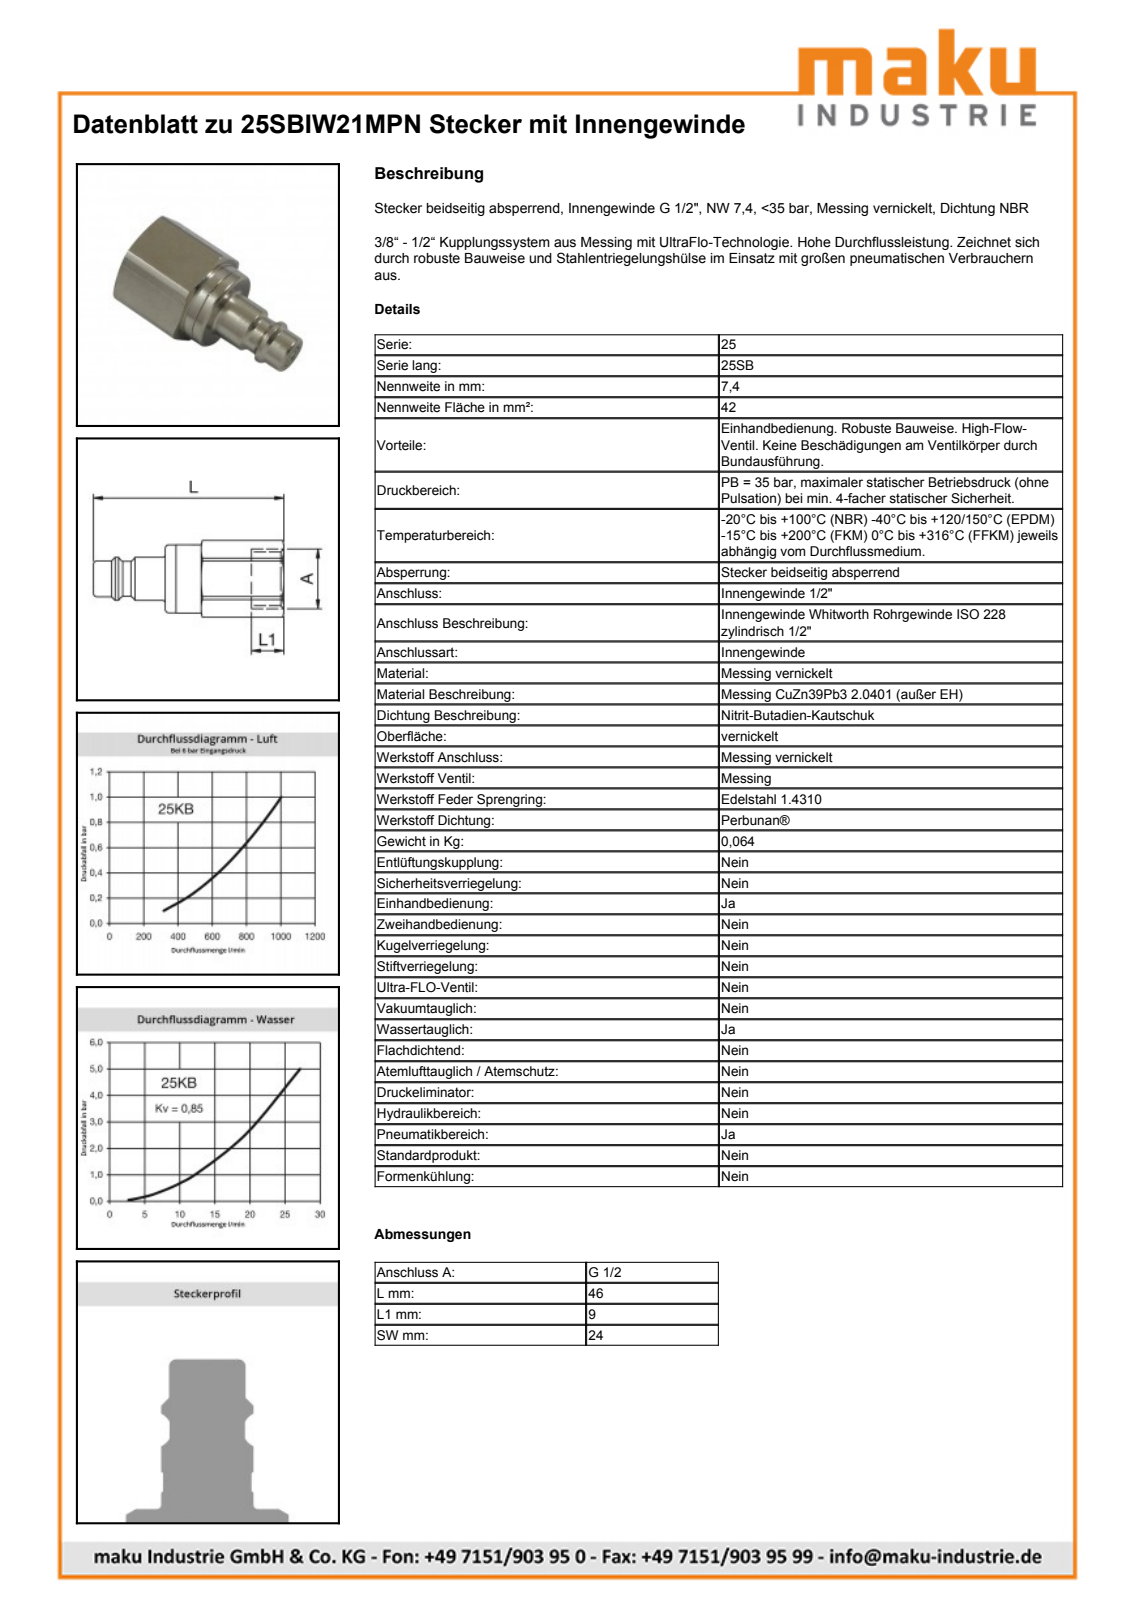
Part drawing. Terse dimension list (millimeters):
name: D108227
written by: Autodesk Inventor 2013 (AUTOMOTIVE_DESIGN)
unit: mm
bodies: 1 solid, 49 faces (14 planar, 15 cylindrical, 20 other)
size: 46.1 × 27.05 × 24.43
volume: 10 627 mm³; area: 4 556 mm²
holes: 1× ⌀17, 1× ⌀18.63
bosses: 1× ⌀21, 1× ⌀18.09, 1× ⌀16.5, 1× ⌀12, 1× ⌀10, 1× ⌀9.75
rounds: 1× R13.53
face distances: 24, 23.98, 26.1, 20, 14.1, 12, 6.1, 8, 34.1, 46.1
